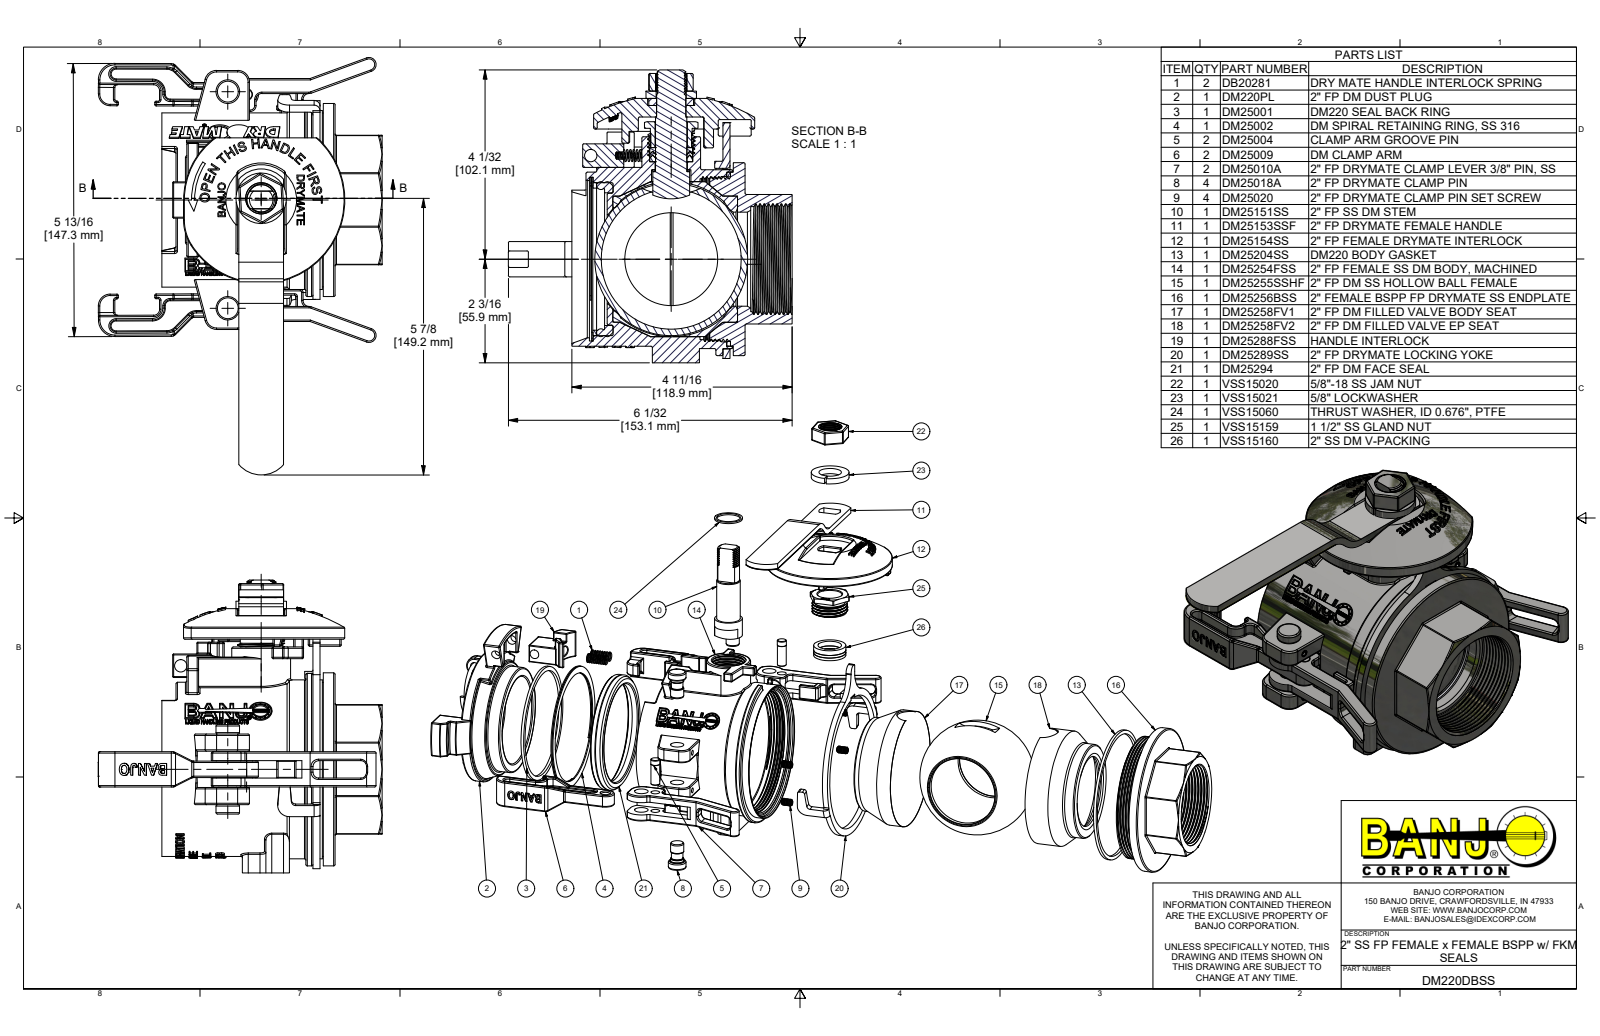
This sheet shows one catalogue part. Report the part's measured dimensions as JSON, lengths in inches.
{"part_name": "DM220DBSS; DM220DBSSX; DM25254FSS; DB20281 (+8 more)", "step_written_by": "Autodesk Inventor 2022 (AUTOMOTIVE_DESIGN)", "units": "inches", "bodies": {"solids": 40, "faces": 4292, "planar": 1456, "cylindrical": 1059, "other": 1777}, "overall_size": [8.865, 6.22, 6.03], "volume_in3": 33.57, "surface_area_in2": 450.9, "round_holes": [[0.145, 4], [0.25, 2], [0.385, 2], [0.18, 1], [0.26, 1], [0.64, 1], [0.662, 1], [0.67, 1], [0.676, 1], [0.69, 1], [0.84, 1], [0.876, 1]], "round_bosses_or_shafts": [[0.19, 4], [0.136, 4], [0.5, 2], [0.375, 2], [0.325, 2], [0.257, 2], [4.22, 1], [4.1, 1]], "partial_cylinders_radius": [[0.03, 406], [0.02, 47], [0.125, 36], [0.06, 27], [0.25, 16], [0.35, 4], [0.7, 3], [0.09, 2]], "face_to_face_distances": [0.15, 0.16, 0.25, 0.31, 0.4, 0.5, 0.39, 0.425, 0.08, 0.47], "hole_center_spacings": [2.369, 4.6, 0.404, 1.134, 2.261, 2.407, 4.558, 4.738]}
